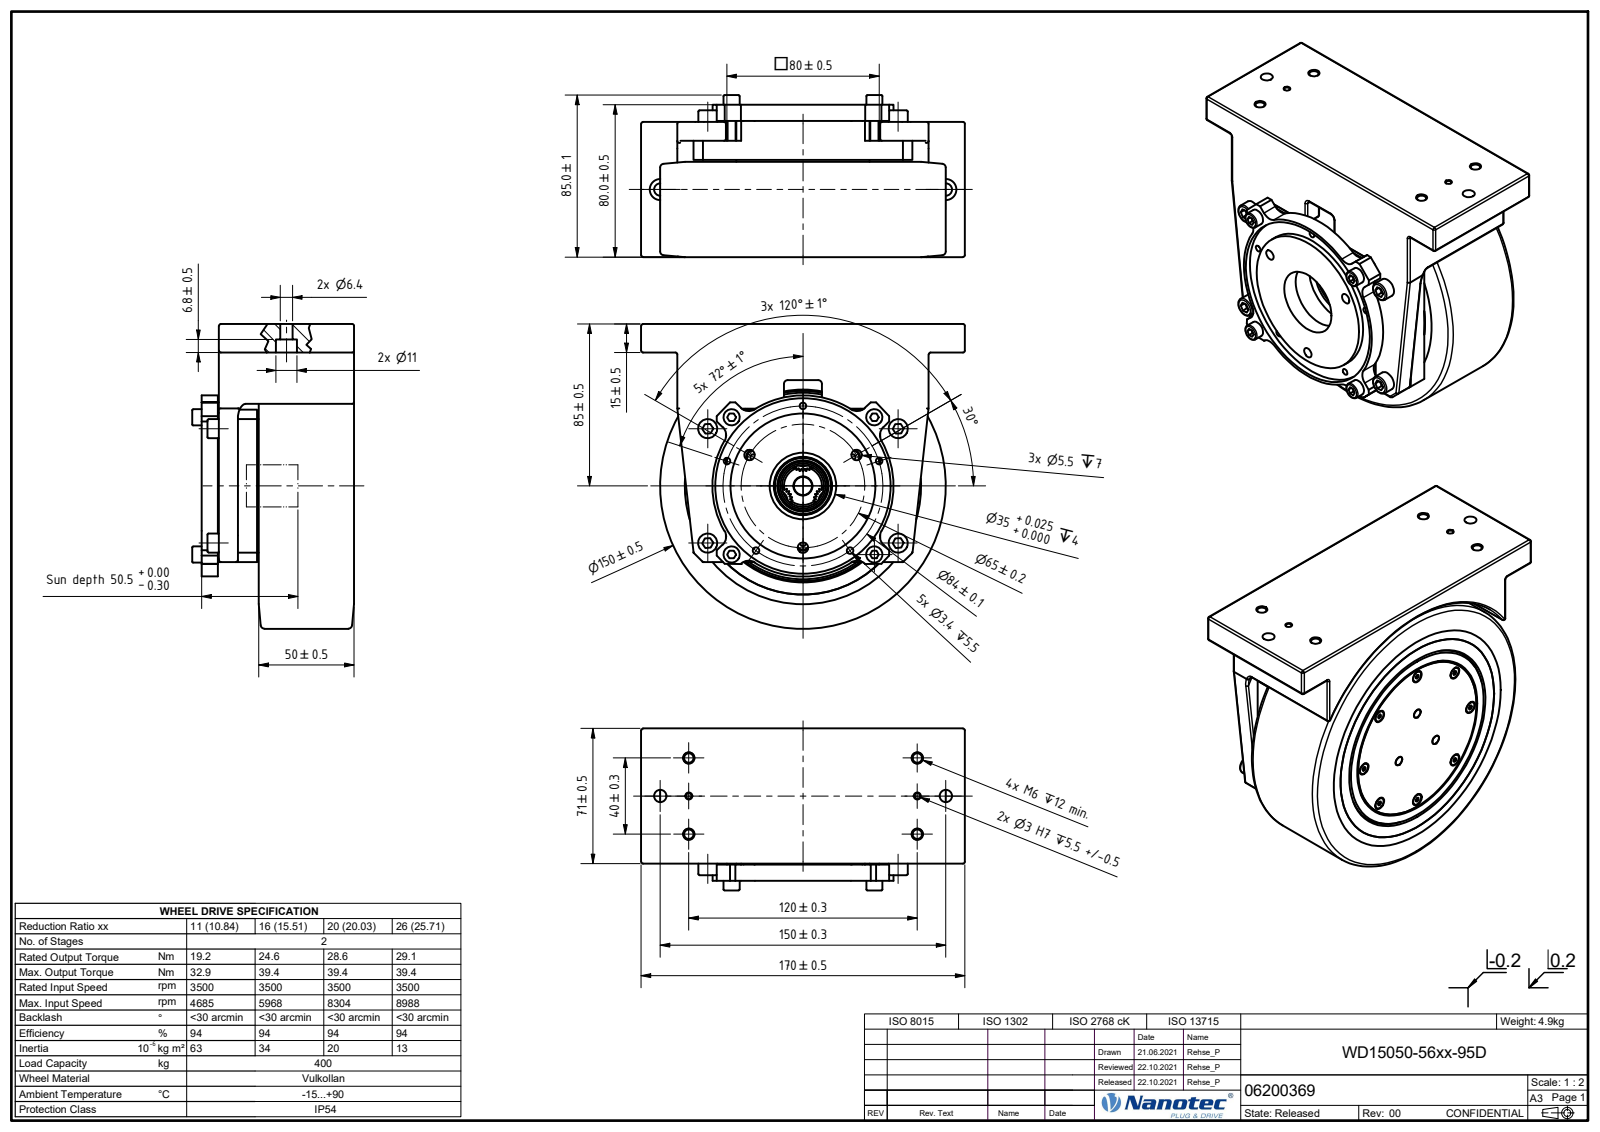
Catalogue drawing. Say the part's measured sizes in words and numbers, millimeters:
The part is named "D-00004078_Shrinkwrap_1". Its 3-D file was written by "Autodesk Inventor 2019 (AUTOMOTIVE_DESIGN)". It is 1 solid with 485 faces: 228 planar, 138 cylindrical and 119 other. Overall it measures 170 by 160 by 85 millimeters. Its volume is 1 362 000 cubic millimeters and its surface area 138 781 square millimeters. Round holes: 8 of diameter 4.92, 7 of diameter 5.5, 5 of diameter 3.4, 4 of diameter 4.13, 3 of diameter 4.97, 2 of diameter 3, 2 of diameter 6.4, 2 of diameter 11, 1 of diameter 35, 1 of diameter 40, 1 of diameter 92. Round bosses or shafts: 8 of diameter 6, 7 of diameter 5, 4 of diameter 10, 4 of diameter 8.5, 1 of diameter 150, 1 of diameter 88, 1 of diameter 76, 1 of diameter 74. Partial cylindrical surfaces (rounded edges, fillets, slot ends): 48 of radius 1, 8 of radius 6, 4 of radius 2, 4 of radius 5, 1 of radius 47.5, 1 of radius 77.5. The main face-to-face distances are 71, 50, 21, 10, 80, 30, 1, 19, 20, 51. The hole center spacings are 28.15, 42, 13.87, 20, 25, 49.37, 51.98, 58.31.
